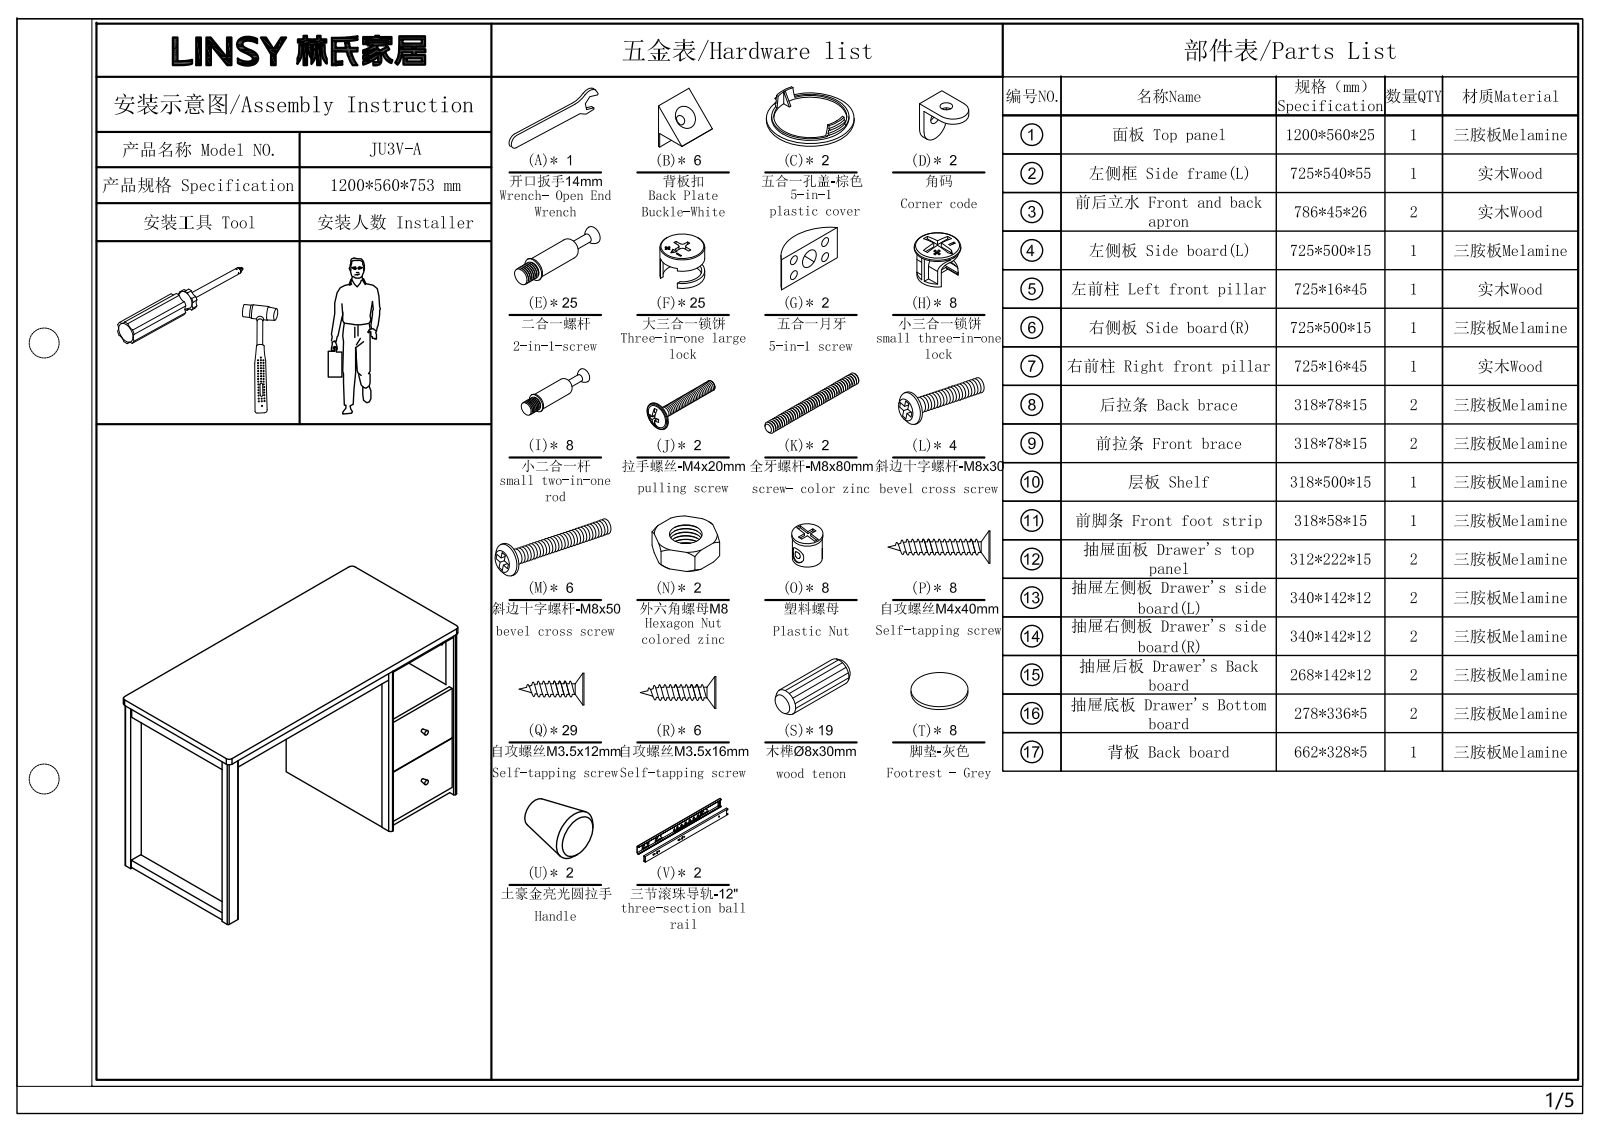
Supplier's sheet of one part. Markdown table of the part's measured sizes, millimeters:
| quantity | value |
| --- | --- |
| STEP written by | ACIS (automotive_design) |
| units | millimeters |
| bodies | 2 solids, 35 faces (9 planar, 16 cylindrical, 10 other) |
| overall size | 110 × 33 × 33 |
| volume | 67 319 mm³ |
| surface area | 18 253 mm² |
| round holes (diameter × count) | 28.24 × 1 |
| round bosses / shafts (diameter × count) | 33 × 1, 25 × 1 |
| partial cylindrical surfaces (radius × count) | 1.8 × 1, 2.96 × 1, 4.07 × 1, 12.49 × 1 |
| main face-to-face distances | 37, 110, 73, 1.16, 75.96, 38.96, 34.04 |
